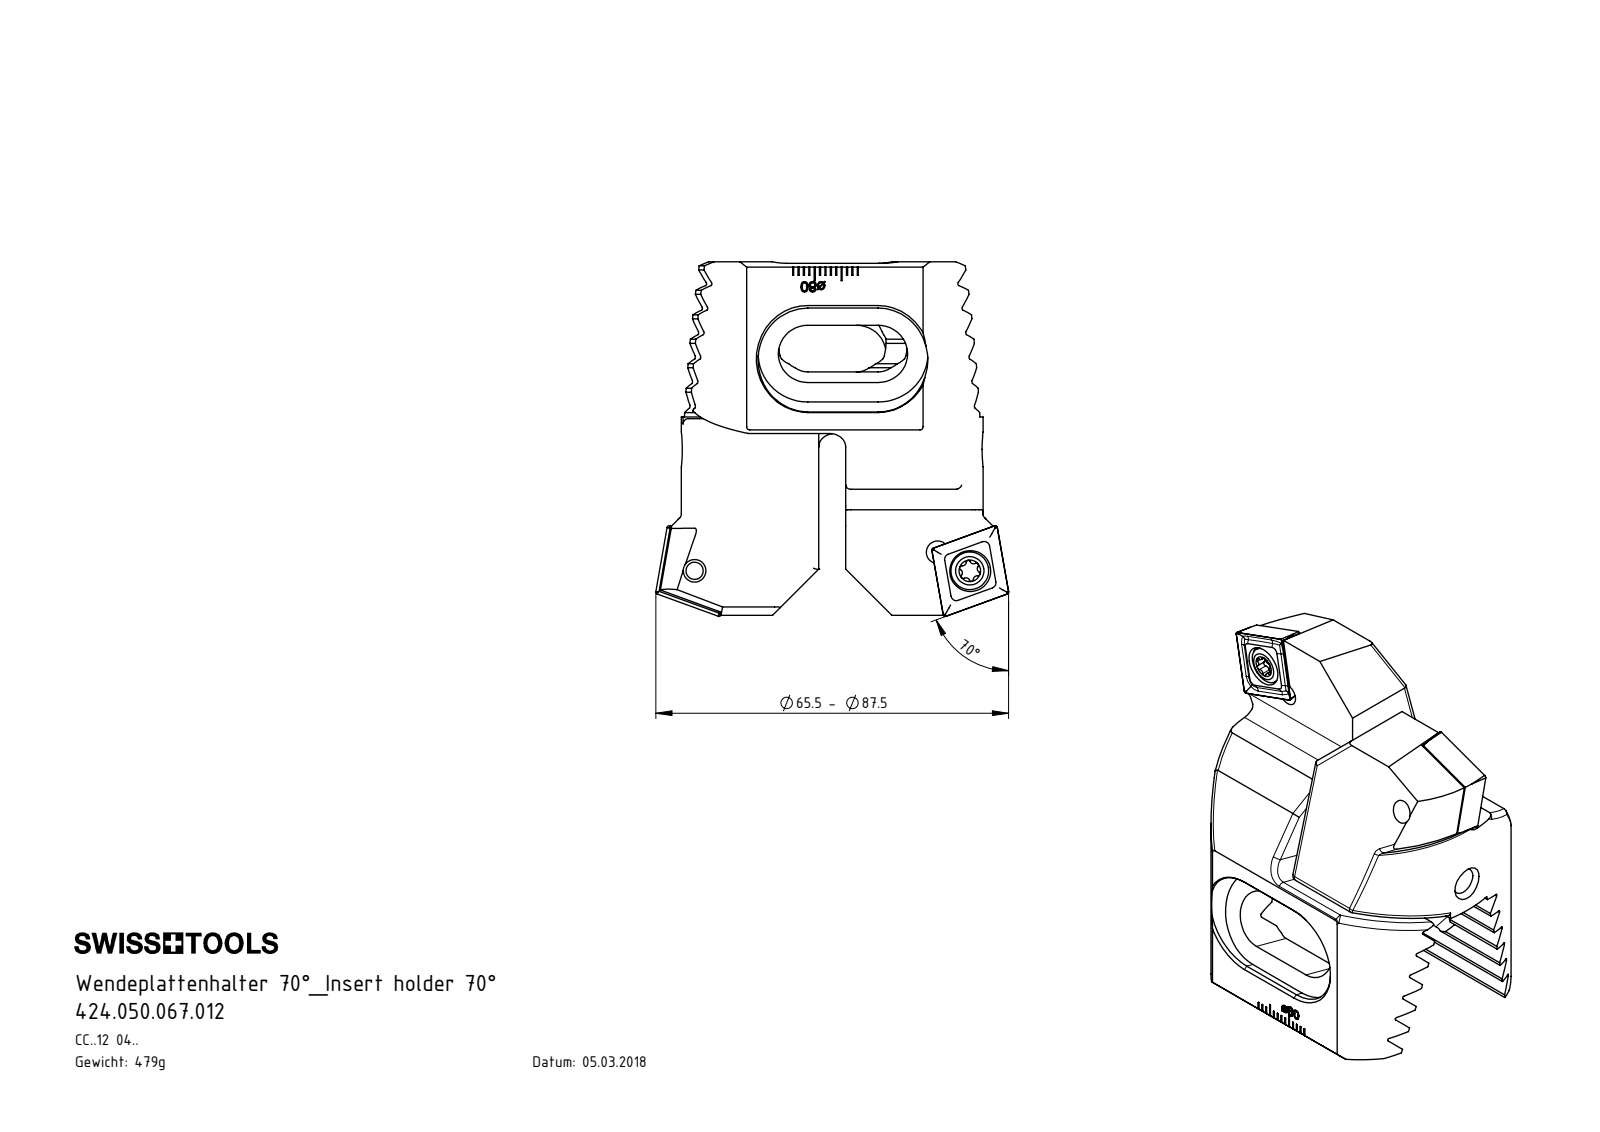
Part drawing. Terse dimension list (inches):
name: CCMT120404; Z55-xxx.001.037_C_CC 12 70ø; WCC-ER2.001.010_A; 424.050.067.012 (+1 more)
written by: SolidWorks 2017 (CONFIG_CONTROL_DESIGN)
unit: in
bodies: 8 solids, 692 faces (336 planar, 132 cylindrical, 224 other)
size: 2.591 × 2.579 × 1.74
volume: 3.776 in³; area: 35.27 in²
holes: 4× ⌀0.165, 2× ⌀0.079, 2× ⌀0.217, 2× ⌀0.299, 1× ⌀0.197
bosses: 2× ⌀0.276, 2× ⌀0.197, 1× ⌀0.236, 1× ⌀0.157
rounds: 14× R0.039, 12× R0.013, 12× R0.015, 8× R0.027, 6× R0.118, 4× R0.027, 4× R0.217, 4× R0.364
face distances: 0.16, 0.32, 0.481, 0.641, 0.801, 0.309, 0.067, 0.858, 0.882, 0.197
hole spacings: 0.271, 0.275, 0.63, 1.781, 1.785, 2.014, 1.217, 1.542
